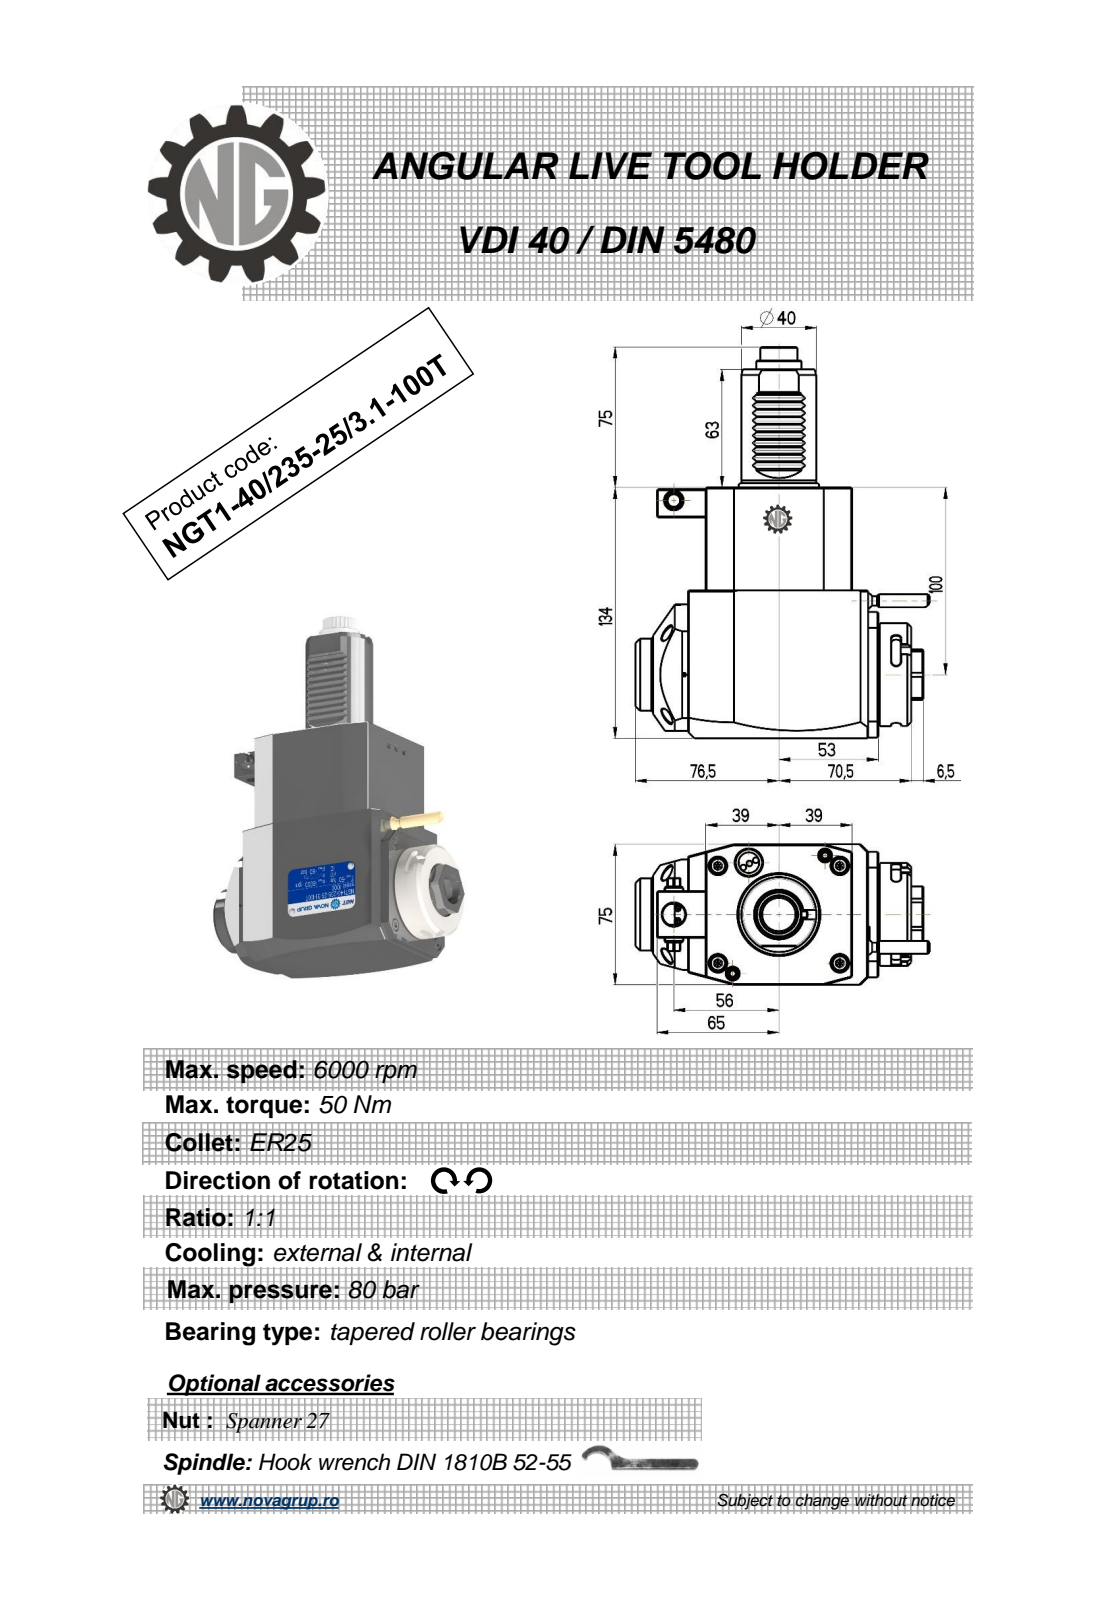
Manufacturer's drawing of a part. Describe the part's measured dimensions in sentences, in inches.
The part is named "NGT1_40_235_25_3_1_100T". Its 3-D file was written by "PRO/ENGINEER BY PARAMETRIC TECHNOLOGY CORPORATION, 2010280 (CONFIG_CONTROL_DESIGN)". It is 1 solid with 462 faces: 186 planar, 180 cylindrical and 96 other. Overall it measures 8.228 by 6.174 by 2.953 inches. Its volume is 66.21 cubic inches and its surface area 120.7 square inches. Round holes: 1 of diameter 0.098, 1 of diameter 0.118, 1 of diameter 0.374, 1 of diameter 0.472, 1 of diameter 0.709. Round bosses or shafts: 2 of diameter 0.315, 1 of diameter 2.165, 1 of diameter 1.89, 1 of diameter 1.575, 1 of diameter 1.516, 1 of diameter 0.945, 1 of diameter 0.394, 1 of diameter 0.276. Partial cylindrical surfaces (rounded edges, fillets, slot ends): 48 of radius 0.082, 10 of radius 0.012, 6 of radius 0.098, 2 of radius 0.591, 2 of radius 7.087, 1 of radius 0.152, 1 of radius 0.167, 1 of radius 0.357. The main face-to-face distances are 2.953, 5.276, 3.071, 0.551, 3.622, 0.689, 1.24, 3.11, 3.342, 4.311. The hole center spacings are 1.701, 2.16, 3.602.
